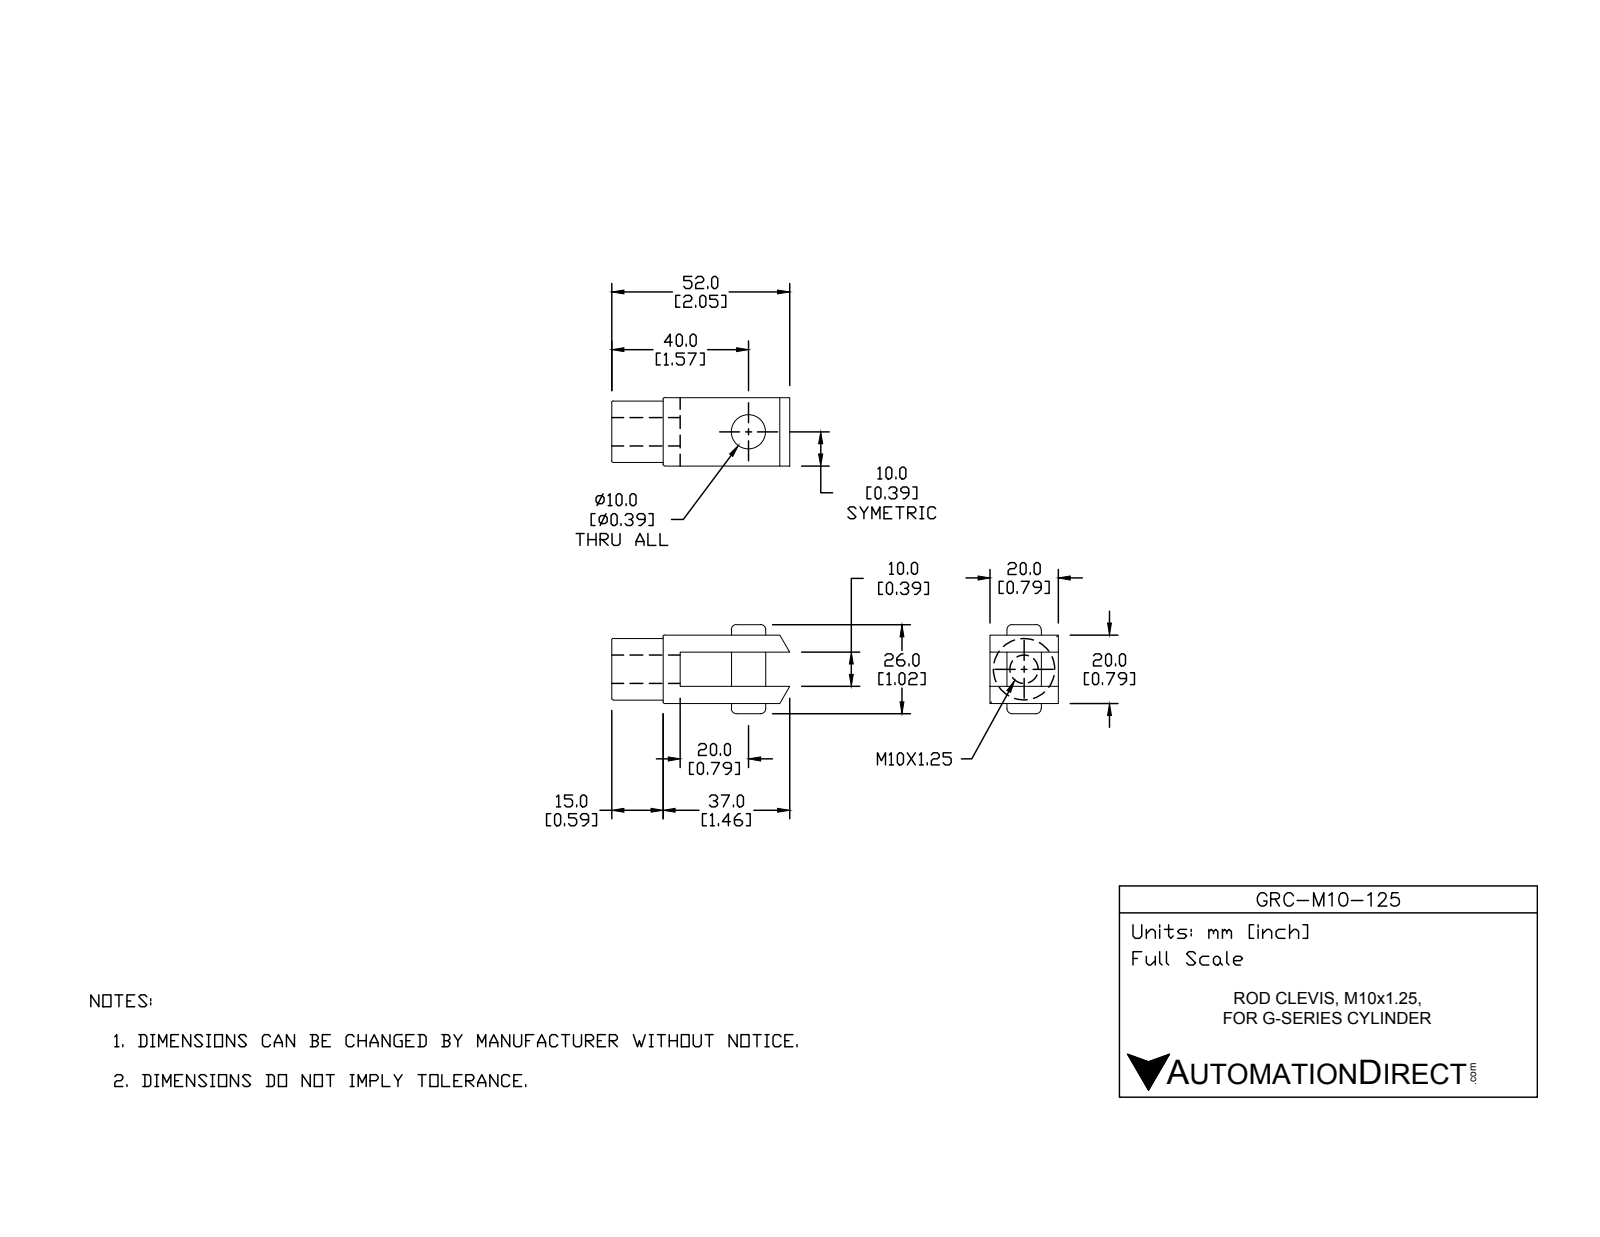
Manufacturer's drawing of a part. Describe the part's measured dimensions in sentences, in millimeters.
The part is named "GRC-M10-125". Its 3-D file was written by "SolidWorks 2017 (AUTOMOTIVE_DESIGN)". It is 1 solid with 36 faces: 16 planar, 14 cylindrical and 6 other. Overall it measures 52 by 26 by 20 millimeters. Its volume is 11 721 cubic millimeters and its surface area 5 779 square millimeters. Round holes: 1 of diameter 8.8. Round bosses or shafts: 1 of diameter 18, 1 of diameter 10. Partial cylindrical surfaces (rounded edges, fillets, slot ends): 4 of radius 1. The main face-to-face distances are 15, 5, 20, 10, 3, 8, 18, 23, 26.
